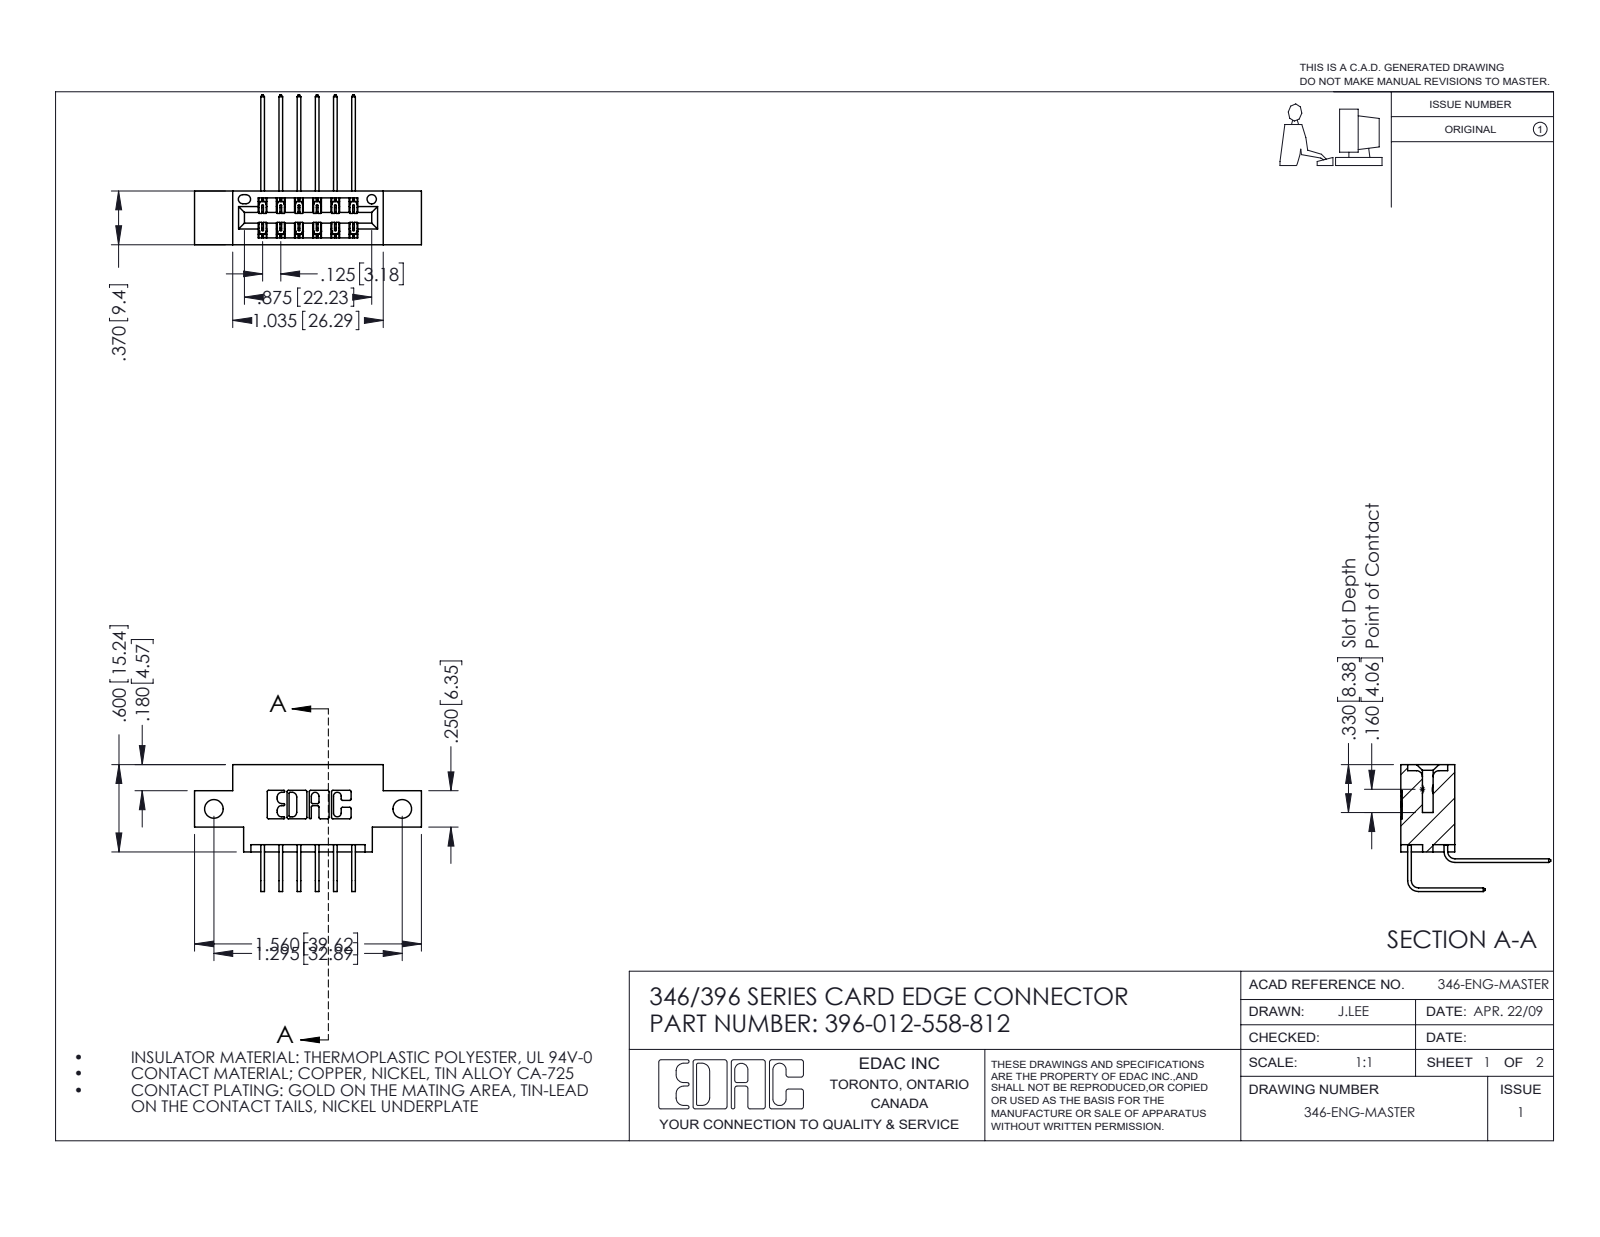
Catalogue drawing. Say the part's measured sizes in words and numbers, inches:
The part is named "396-012-558-812; 345-292-001_558 559 Tail - 1; 345-292-001_558 Tail - 2; 346 Part_0.170 Offset - Side Mount". Its 3-D file was written by "SolidWorks 2016 (CONFIG_CONTROL_DESIGN)". It is 13 solids with 774 faces: 524 planar, 250 cylindrical and 0 other. Overall it measures 1.56 by 1.03 by 0.873 inches. Its volume is 0.208 cubic inches and its surface area 6.972 square inches. Round holes: 2 of diameter 0.128, 1 of diameter 0.064. Partial cylindrical surfaces (rounded edges, fillets, slot ends): 22 of radius 0.01, 18 of radius 0.006, 6 of radius 0.007, 6 of radius 0.031, 3 of radius 0.026, 2 of radius 0.014, 2 of radius 0.022, 2 of radius 0.024. The main face-to-face distances are 0.25, 0.37, 0.048, 0.322, 0.025, 0.072, 0.298, 0.148, 0.222, 0.1. The hole center spacings are 1.295.
